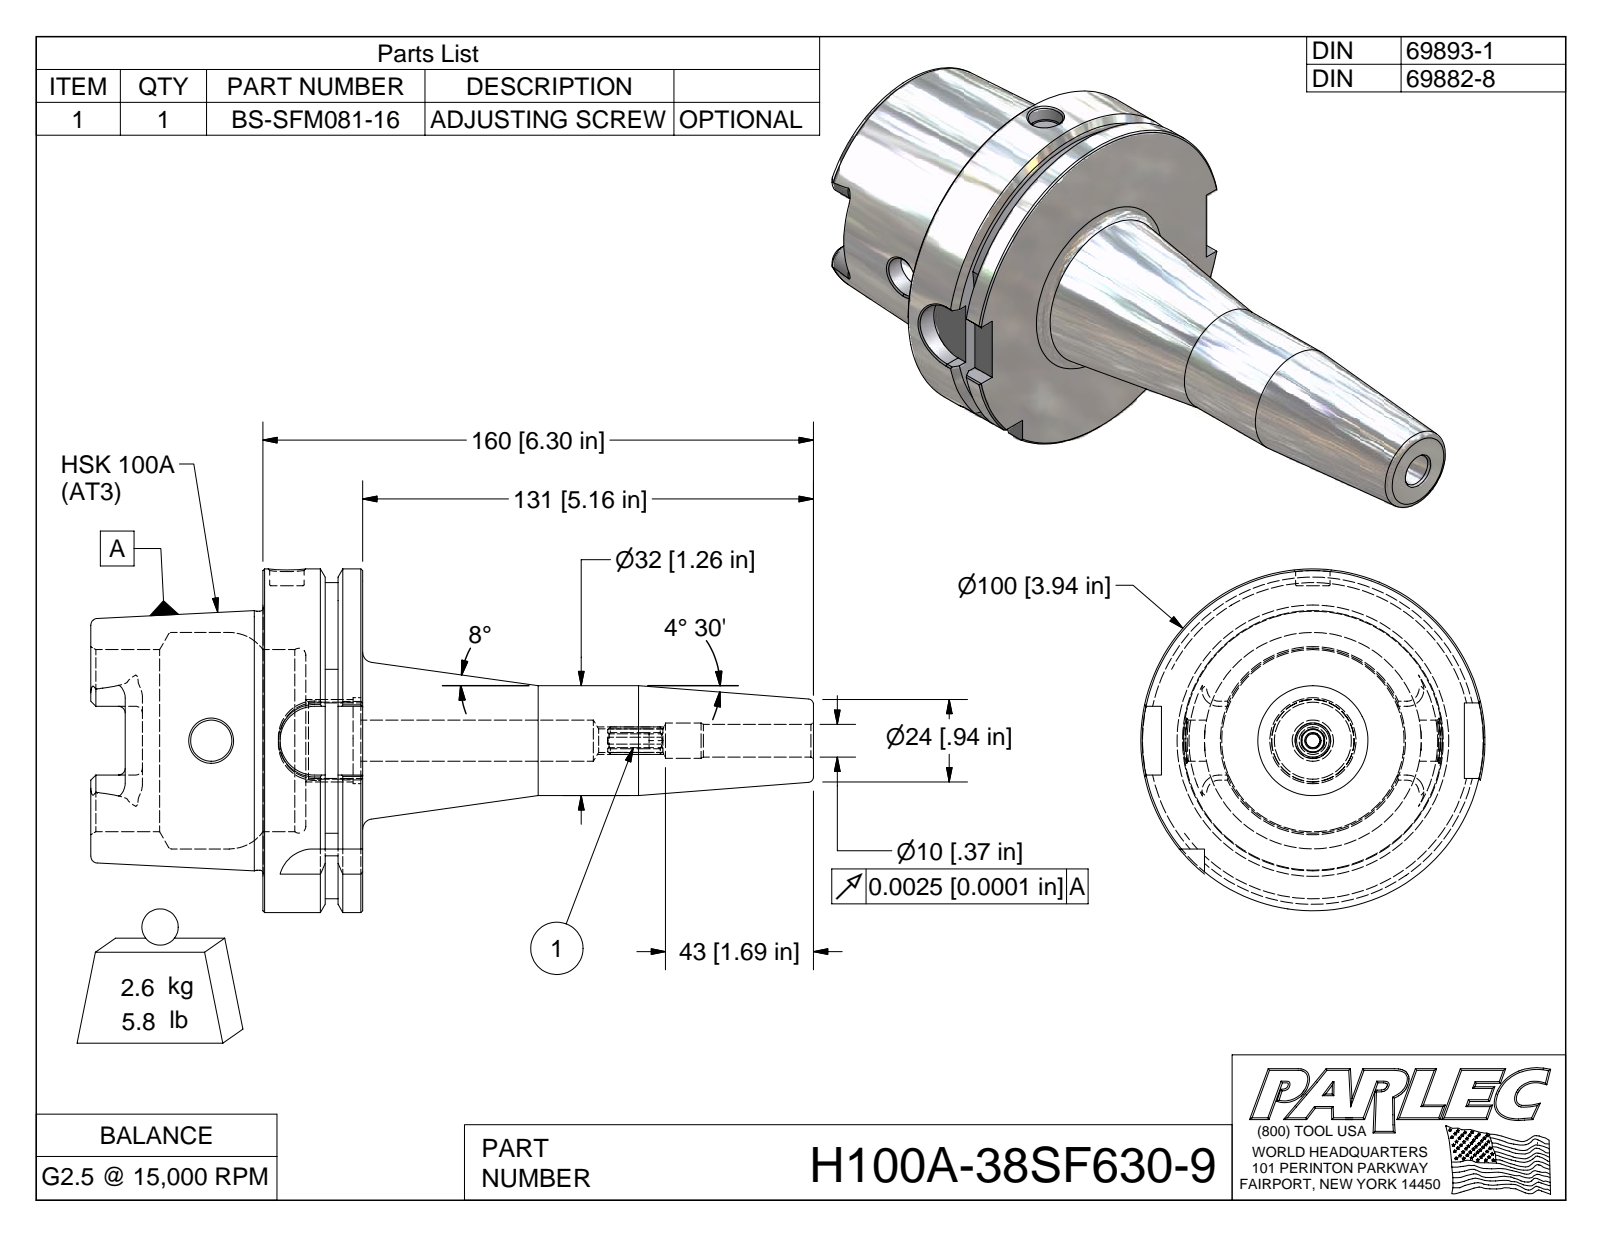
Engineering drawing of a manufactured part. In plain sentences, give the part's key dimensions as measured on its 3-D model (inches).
The part is named "H100A-38SF630-9; H100A-38SF630-9-1; BS-SFM081-16". Its 3-D file was written by "Autodesk Inventor 2009 (AUTOMOTIVE_DESIGN)". It is 2 solids with 150 faces: 49 planar, 30 cylindrical and 71 other. Overall it measures 8.269 by 3.937 by 3.937 inches. Its volume is 21.97 cubic inches and its surface area 104.3 square inches. Round holes: 1 of diameter 0.374, 1 of diameter 0.394, 1 of diameter 0.404, 1 of diameter 0.472, 1 of diameter 0.881, 1 of diameter 0.985, 1 of diameter 2.087, 1 of diameter 2.48. Round bosses or shafts: 1 of diameter 3.937, 1 of diameter 2.967, 1 of diameter 1.26. Partial cylindrical surfaces (rounded edges, fillets, slot ends): 4 of radius 0.394, 3 of radius 0.079, 2 of radius 0.192, 1 of radius 0.157, 1 of radius 1.811. The main face-to-face distances are 1.142, 0.492, 0.65, 1.969, 2.461, 3.11, 2.682, 0.713, 0.221, 0.428.
